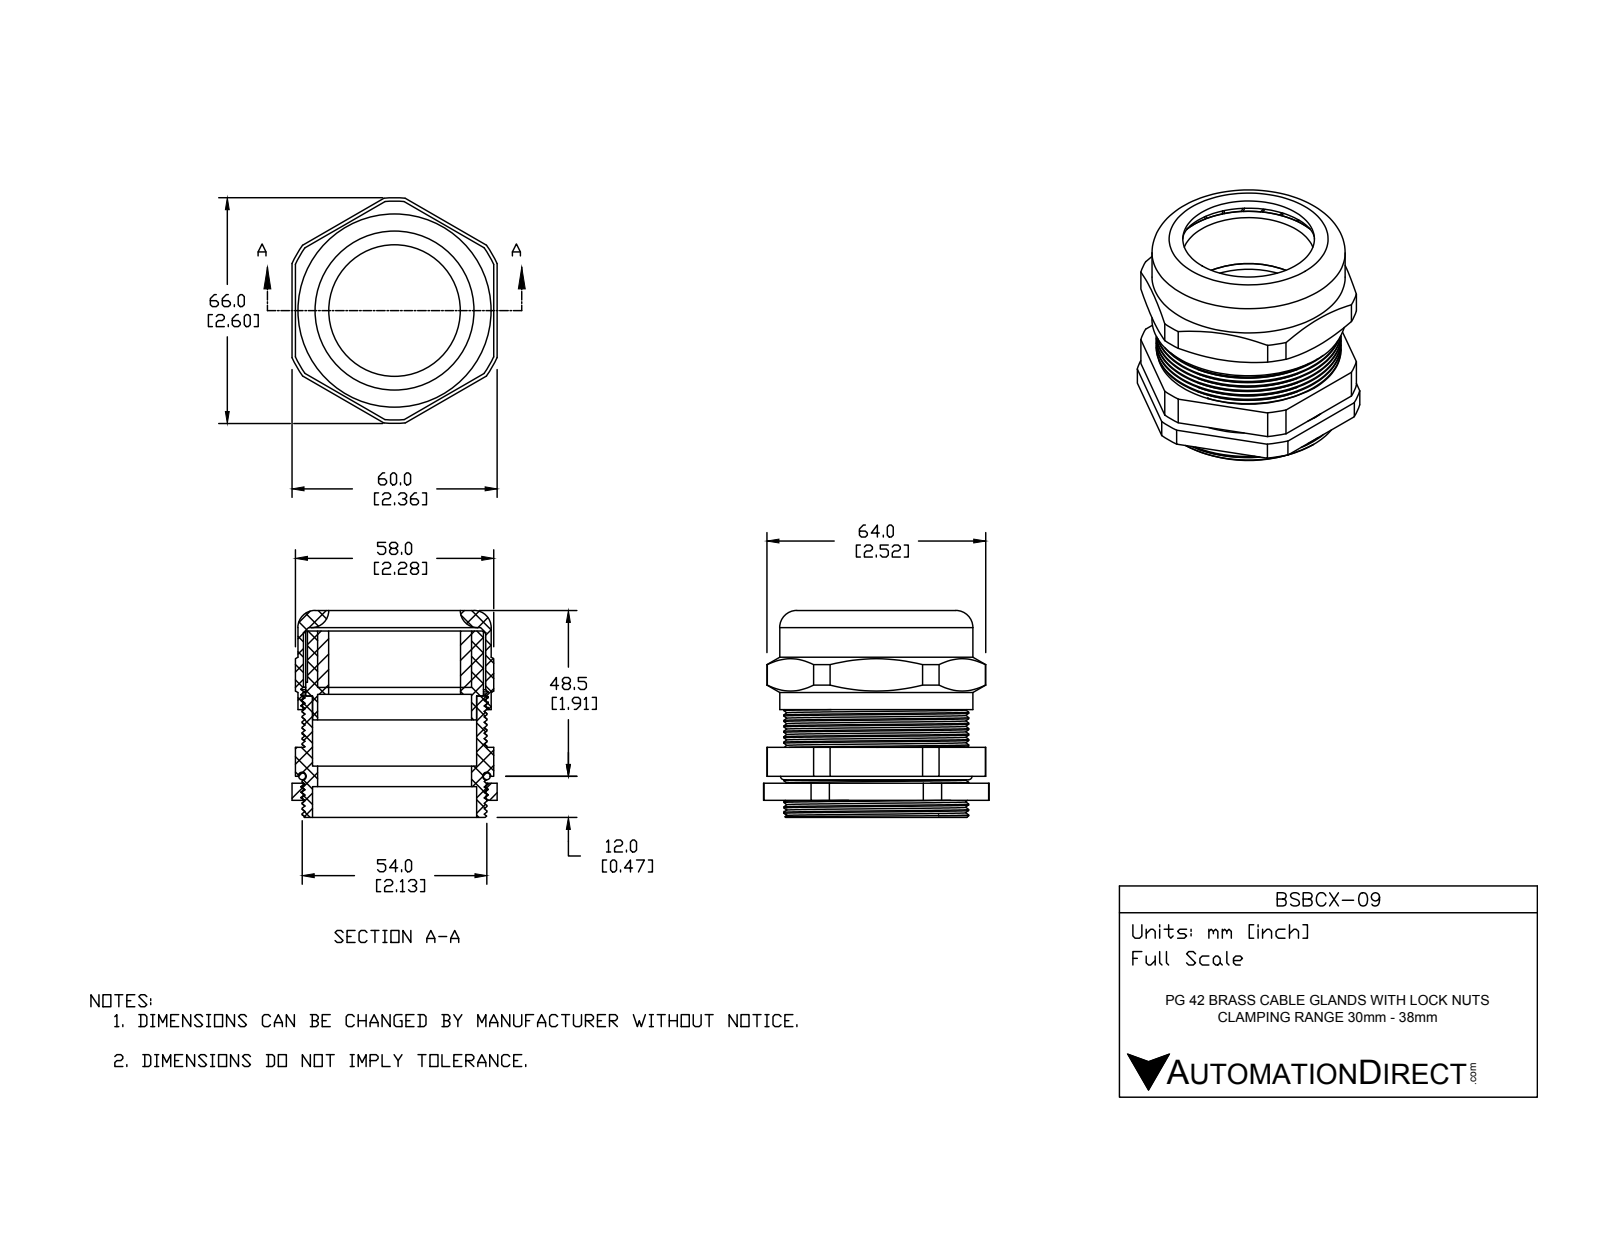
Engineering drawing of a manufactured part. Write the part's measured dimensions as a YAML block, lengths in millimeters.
part_name: "BSBCX-09"
step_written_by: "SolidWorks 2015 (CONFIG_CONTROL_DESIGN)"
units: millimeters
bodies: {solids: 6, faces: 262, planar: 137, cylindrical: 95, other: 30}
overall_size: [66, 60.5, 60]
volume: 59743
surface_area: 51268
round_holes:
  - {diameter: 38.6, count: 1}
  - {diameter: 45, count: 1}
  - {diameter: 48, count: 1}
  - {diameter: 53.33, count: 1}
round_bosses_or_shafts:
  - {diameter: 56.5, count: 1}
  - {diameter: 54, count: 1}
  - {diameter: 52, count: 1}
partial_cylinders:
  - {radius: 32, count: 1}
  - {radius: 33, count: 1}
face_to_face_distances: [0.5, 5, 58, 16.5, 1, 15.5, 26, 15, 59, 2]
